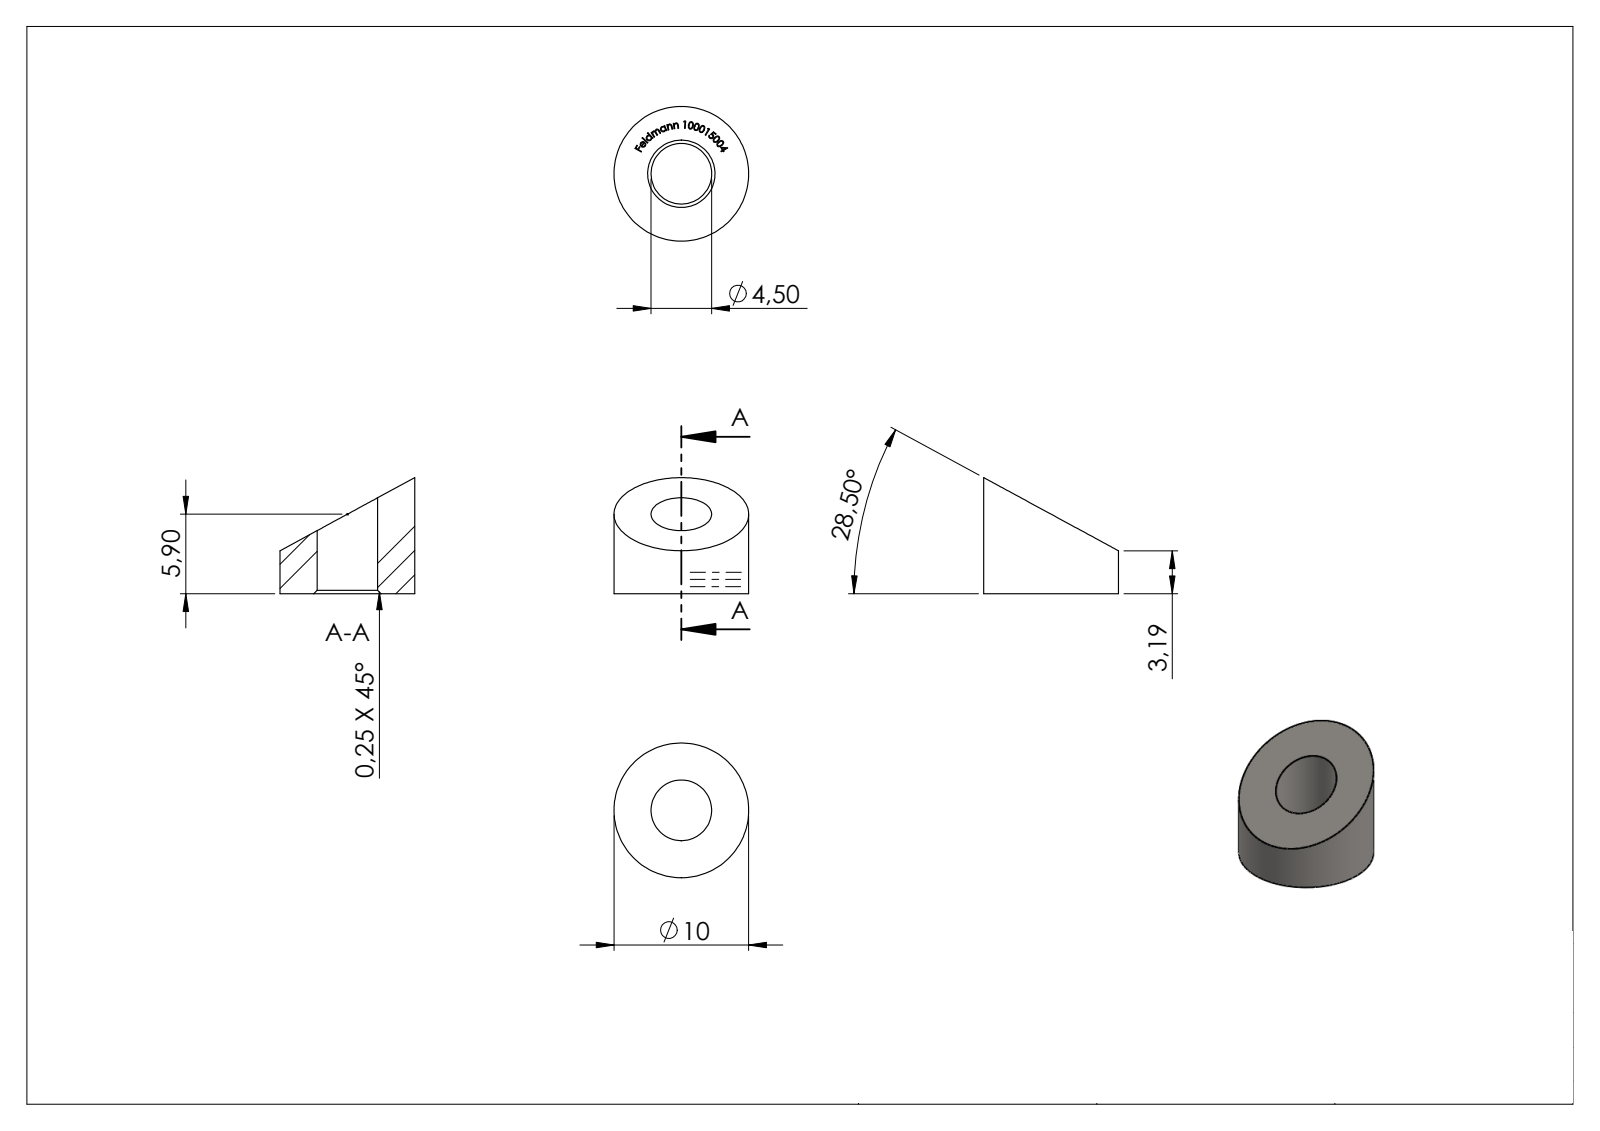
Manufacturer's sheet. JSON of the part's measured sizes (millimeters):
{"part_name": "100015004", "step_written_by": "SolidWorks 2015 (CONFIG_CONTROL_DESIGN)", "units": "millimeters", "bodies": {"solids": 1, "faces": 220, "planar": 113, "cylindrical": 4, "other": 103}, "overall_size": [10, 10, 8.61], "volume_mm3": 369, "surface_area_mm2": 405, "round_holes": [[4.5, 1]], "round_bosses_or_shafts": [[10, 1]], "face_to_face_distances": [0.34, 0.53, 0.58, 0.39, 0.54, 0.48, 0.35, 1.26]}
